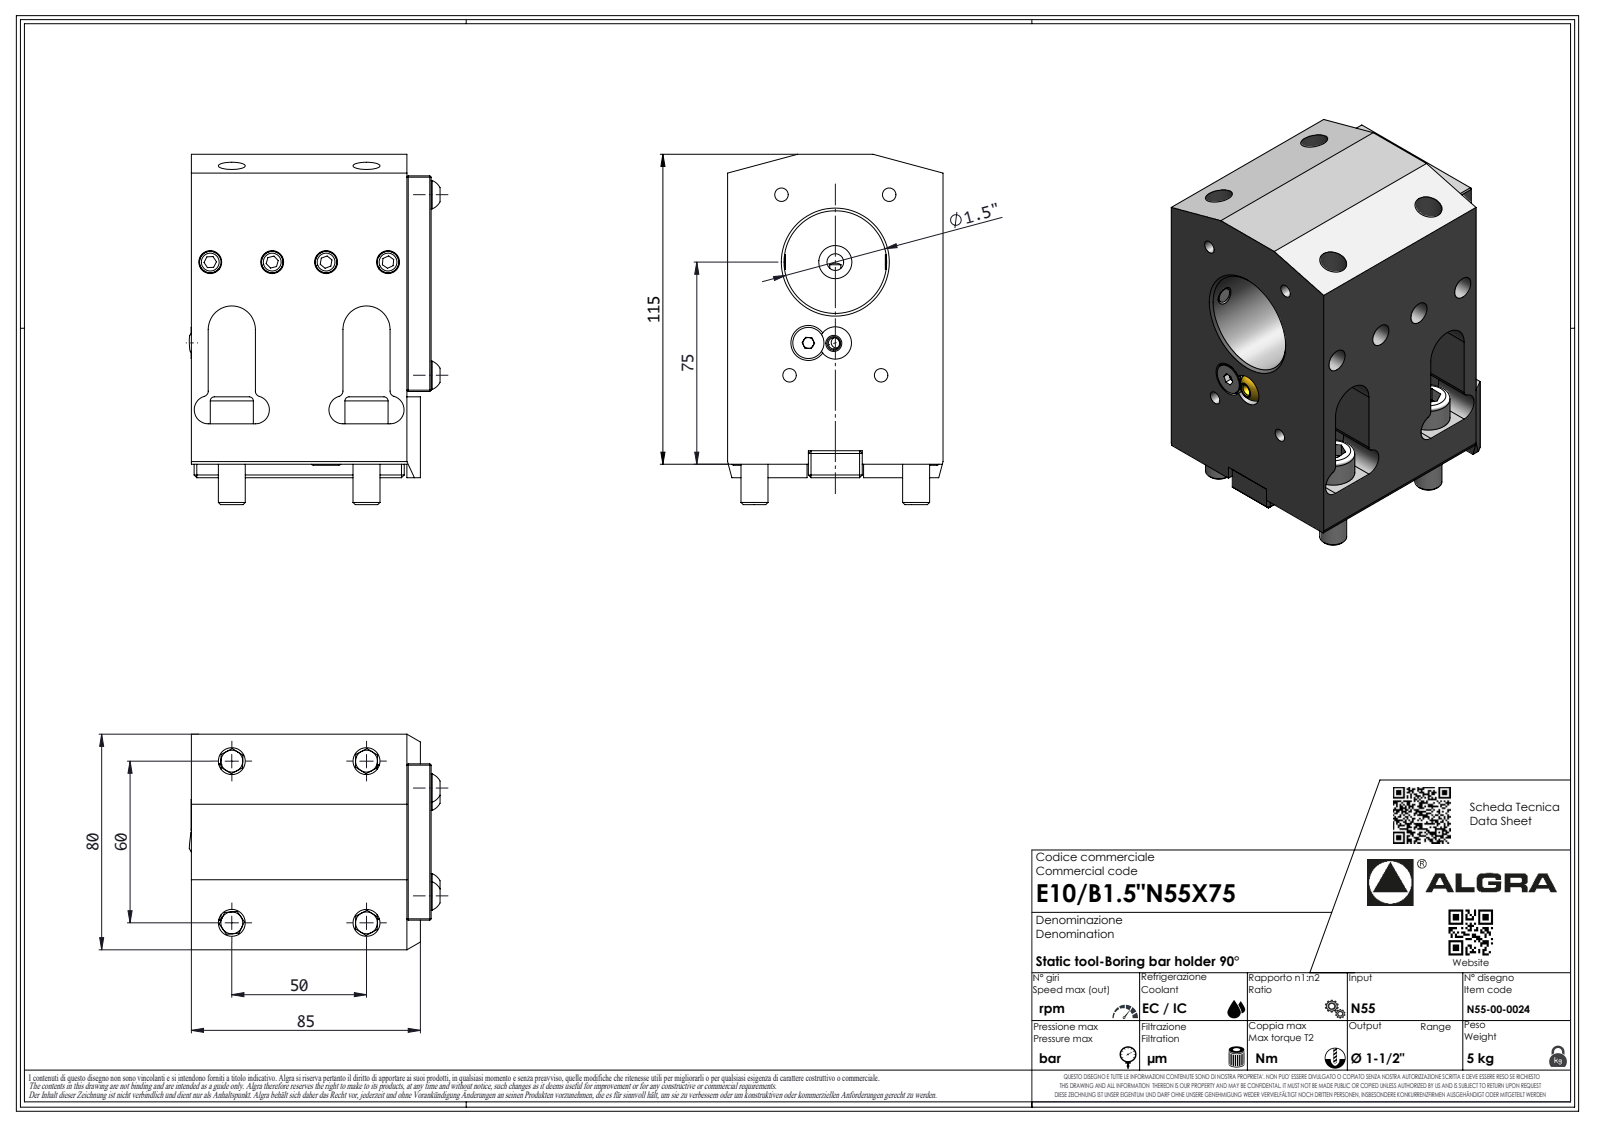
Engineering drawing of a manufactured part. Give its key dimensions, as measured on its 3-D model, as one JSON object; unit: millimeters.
{"part_name": "E10B1.5N55X75", "step_written_by": "SolidWorks 2023 (AUTOMOTIVE_DESIGN)", "units": "millimeters", "bodies": {"solids": 1, "faces": 434, "planar": 307, "cylindrical": 59, "other": 68}, "overall_size": [130, 89.79, 80], "volume_mm3": 648815, "surface_area_mm2": 76583, "round_holes": [[2.1, 1], [38.1, 1]], "round_bosses_or_shafts": [[16, 4], [10, 4], [6.37, 1], [1.7, 1]], "partial_cylinders_radius": [[0.33, 7], [0.52, 7], [3.7, 7], [2, 4], [5.2, 4], [8.75, 2], [10.5, 2], [0.21, 1]], "face_to_face_distances": [80, 89, 5, 18.5, 61.5, 50, 6.25, 73.75, 9, 30]}
